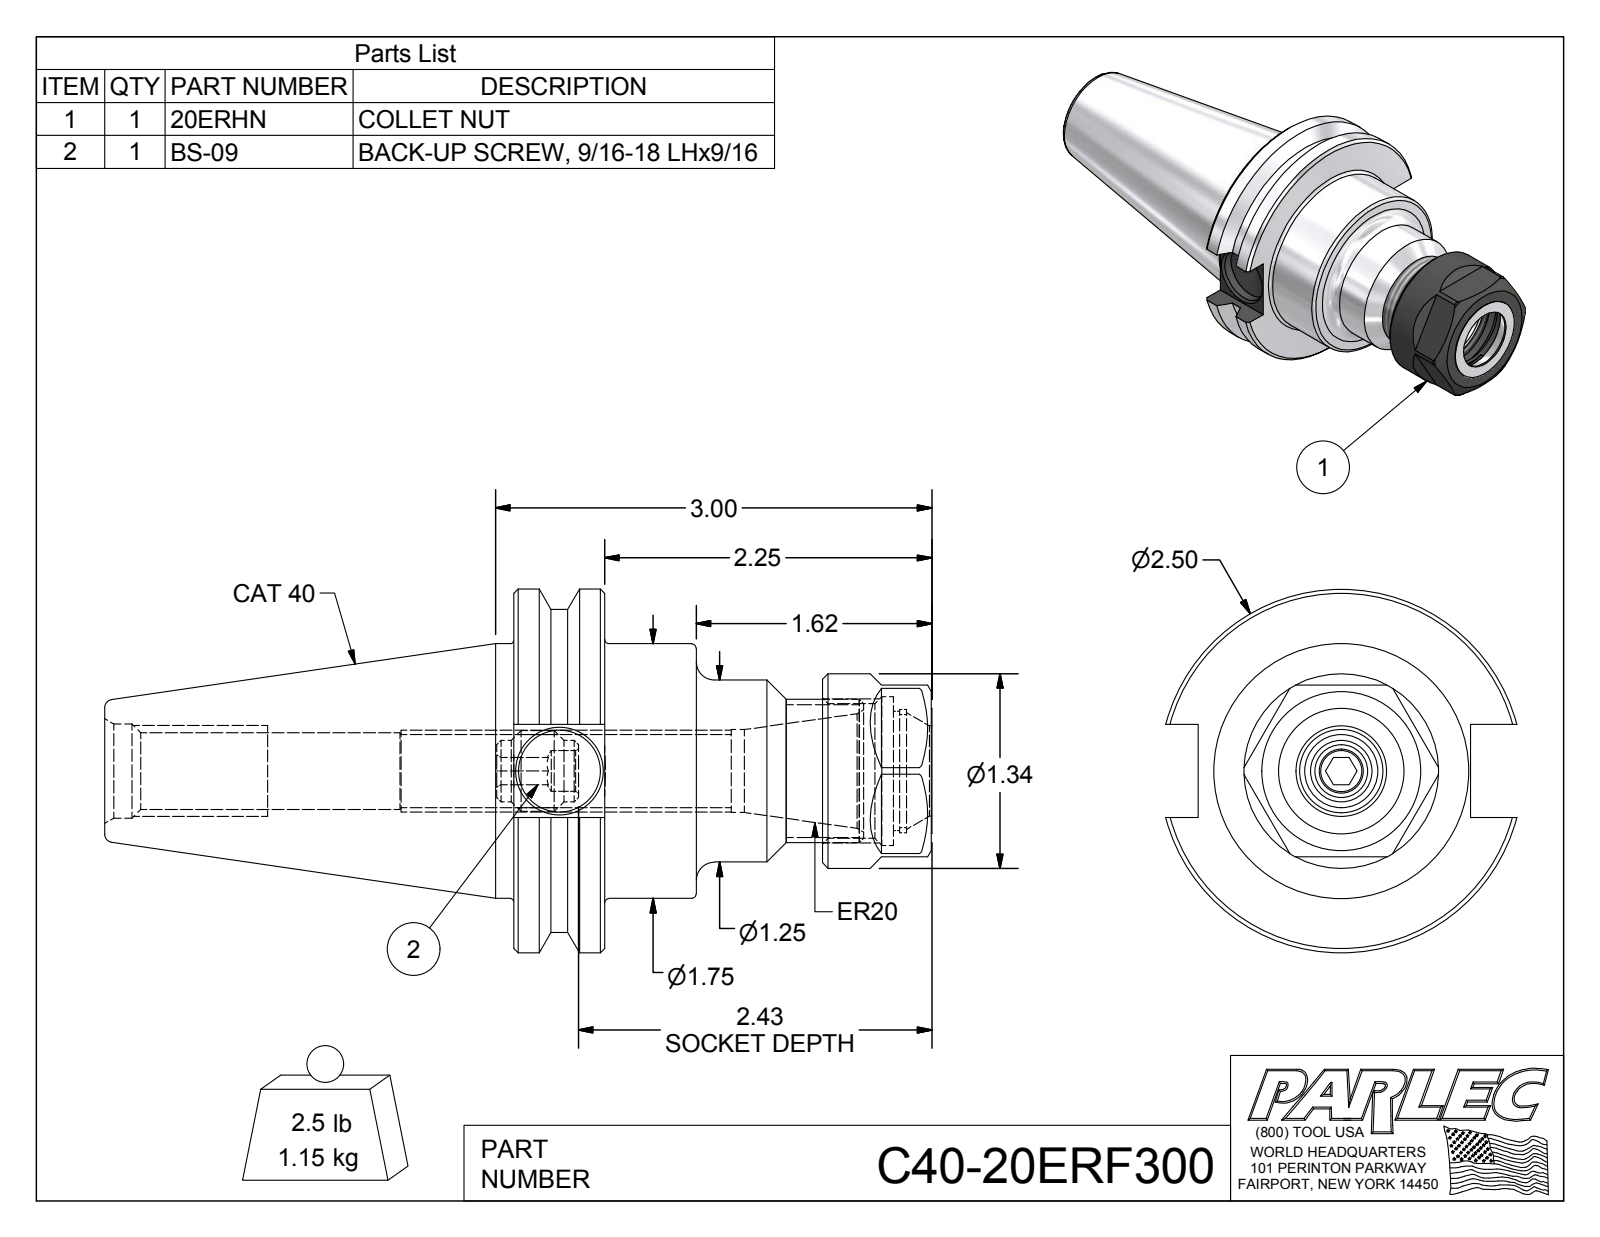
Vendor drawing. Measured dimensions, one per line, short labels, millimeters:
name: C40-20ER3-1; 20ERHN; BS-09; C40-20ERF300
written by: Autodesk Inventor 2016 (AUTOMOTIVE_DESIGN)
unit: mm
bodies: 3 solids, 111 faces (44 planar, 27 cylindrical, 40 other)
size: 144.46 × 63.5 × 61.38
volume: 146 039 mm³; area: 32 028 mm²
holes: 1× ⌀7.14, 1× ⌀8, 1× ⌀10.13, 1× ⌀12.75, 1× ⌀13.39, 1× ⌀14.48, 1× ⌀15.49, 1× ⌀16.46, 1× ⌀23.5, 1× ⌀26
bosses: 1× ⌀63.5, 1× ⌀56.36, 1× ⌀44.45, 1× ⌀34, 1× ⌀31.75, 1× ⌀25, 1× ⌀14.1, 1× ⌀10.72
rounds: 1× R9.47, 1× R10.55, 1× R10.75
face distances: 15.88, 73.03, 57.15, 30, 31.88, 16, 41.15, 53.96, 38.08, 22.08
